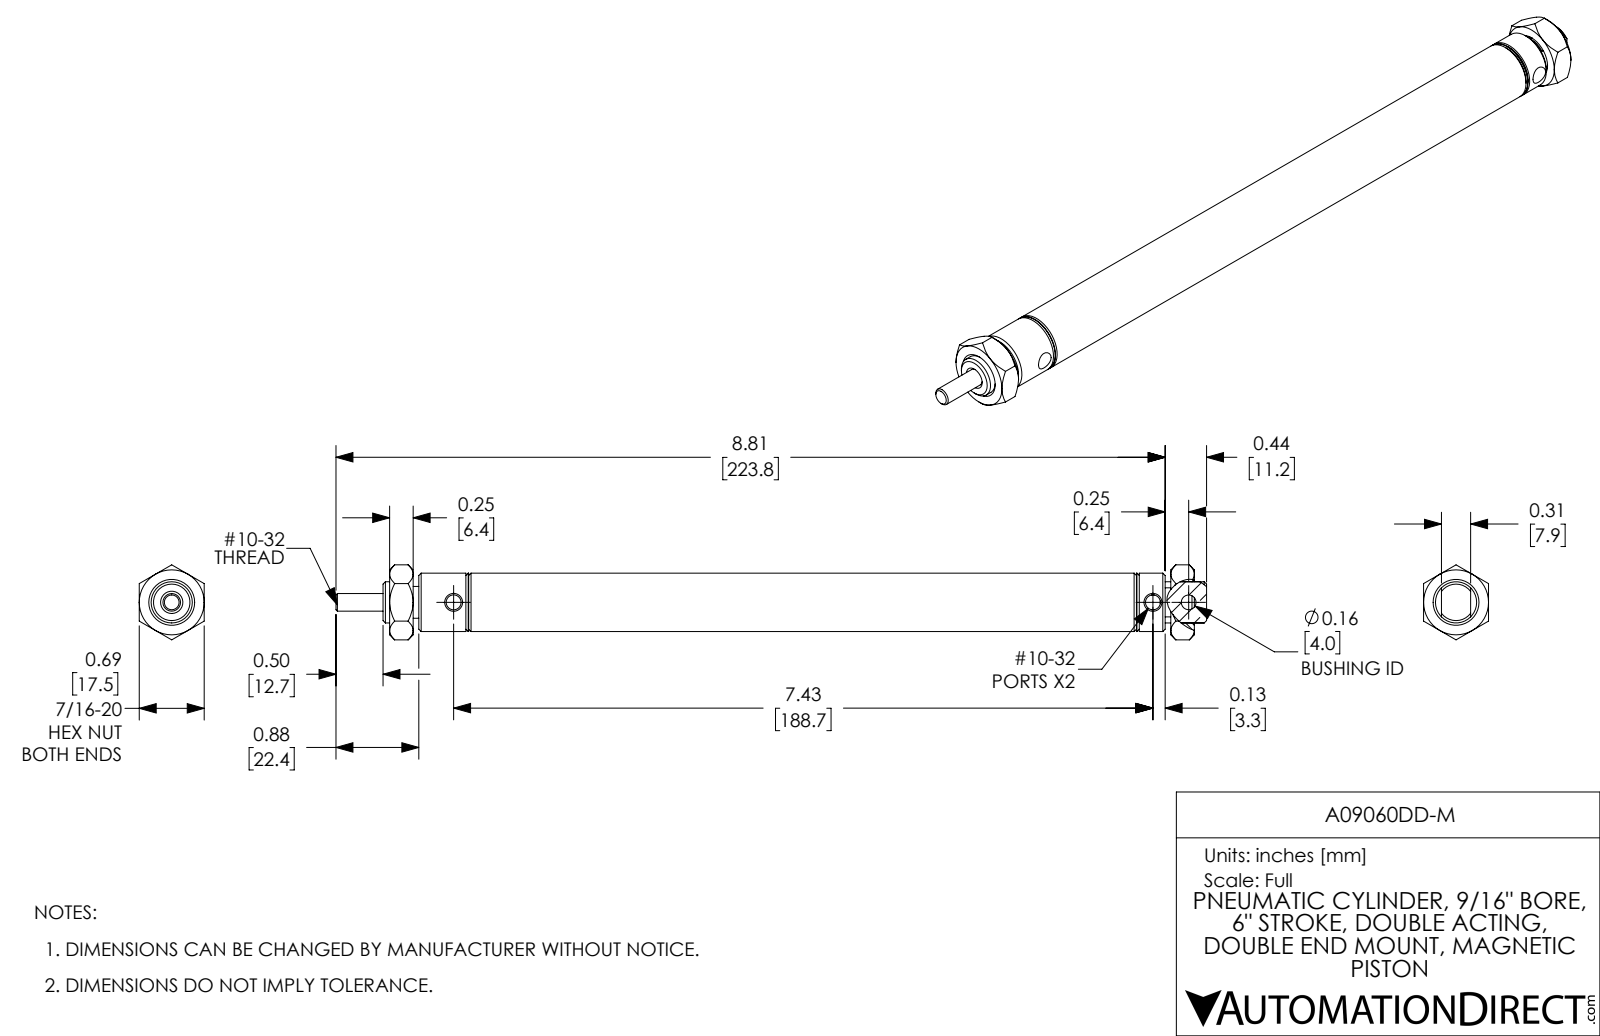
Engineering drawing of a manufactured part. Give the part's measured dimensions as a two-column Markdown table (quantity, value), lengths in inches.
| quantity | value |
| --- | --- |
| part name | A09060DD-M; A09060DD-M_Mounting Nut_D-154; A09060DD-M-Rod; A09060DD-M-MainBody |
| STEP written by | SolidWorks 2017 (AUTOMOTIVE_DESIGN) |
| units | inches |
| bodies | 4 solids, 151 faces (36 planar, 46 cylindrical, 69 other) |
| overall size | 9.25 × 0.797 × 0.69 |
| volume | 1.28 in³ |
| surface area | 39.15 in² |
| round holes (diameter × count) | 0.159 × 2, 0.19 × 2, 0.156 × 1, 0.157 × 1, 0.187 × 1, 0.563 × 1 |
| round bosses / shafts (diameter × count) | 0.62 × 1, 0.437 × 1, 0.338 × 1 |
| main face-to-face distances | 0.69, 0.5, 0.25, 8.3, 0.715, 7.215, 7.275, 0.31, 6.5, 0.775 |
| hole center spacings | 0.38, 7.43, 7.81 |
